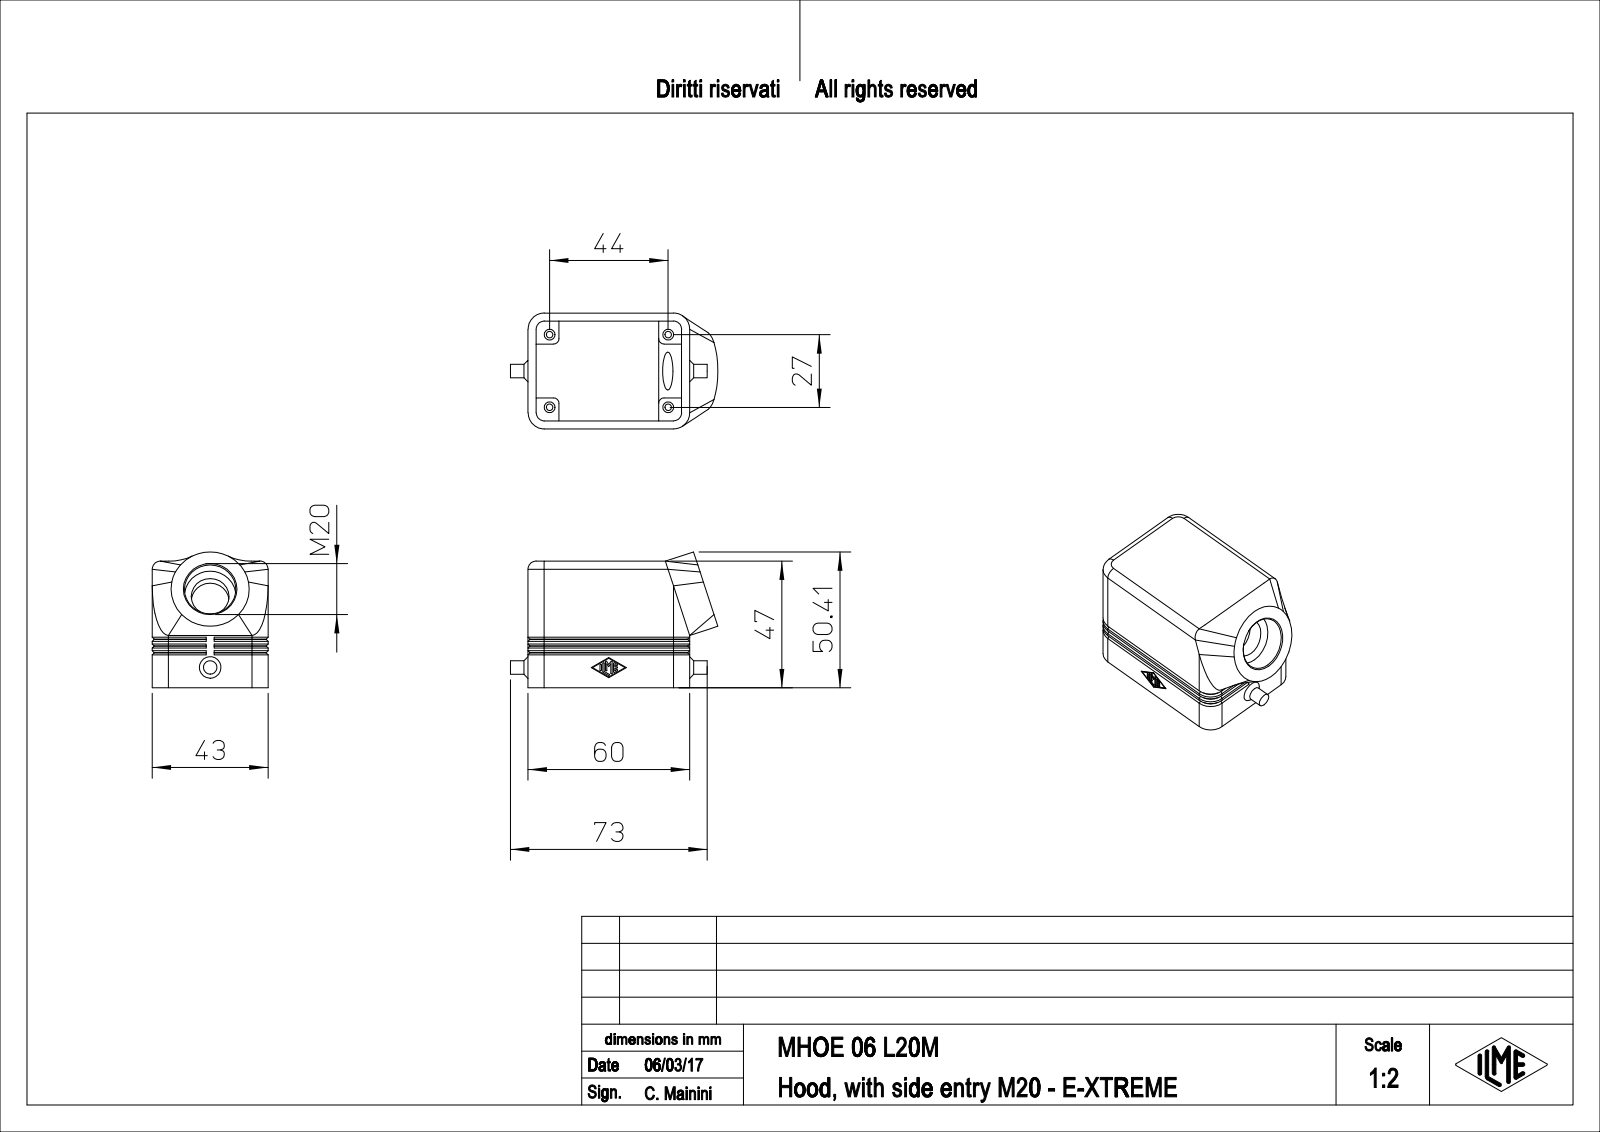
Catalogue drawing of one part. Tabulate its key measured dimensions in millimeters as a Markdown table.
| quantity | value |
| --- | --- |
| part name | MHOE_06_L20M |
| STEP written by | PTC Creo Elements/Direct Modeling 19.0E 27-Jun-2016 (C) Parametric Technology GmbH (AUTOMOTIVE_DESIGN) |
| units | millimeters |
| bodies | 1 solid, 269 faces (140 planar, 77 cylindrical, 52 other) |
| overall size | 76.96 × 50.41 × 43 |
| volume | 45 431 mm³ |
| surface area | 23 358 mm² |
| round holes (diameter × count) | 2.46 × 4, 4 × 4, 14.06 × 1, 19.06 × 1 |
| round bosses / shafts (diameter × count) | 5 × 1 |
| partial cylindrical surfaces (radius × count) | 0.25 × 14, 3 × 7, 2 × 4, 5.3 × 4, 6 × 4 |
| main face-to-face distances | 3, 40, 37, 43, 11.5, 8.5, 48.5, 45.5, 57, 31.5 |
| hole center spacings | 27, 44, 51.62 |
